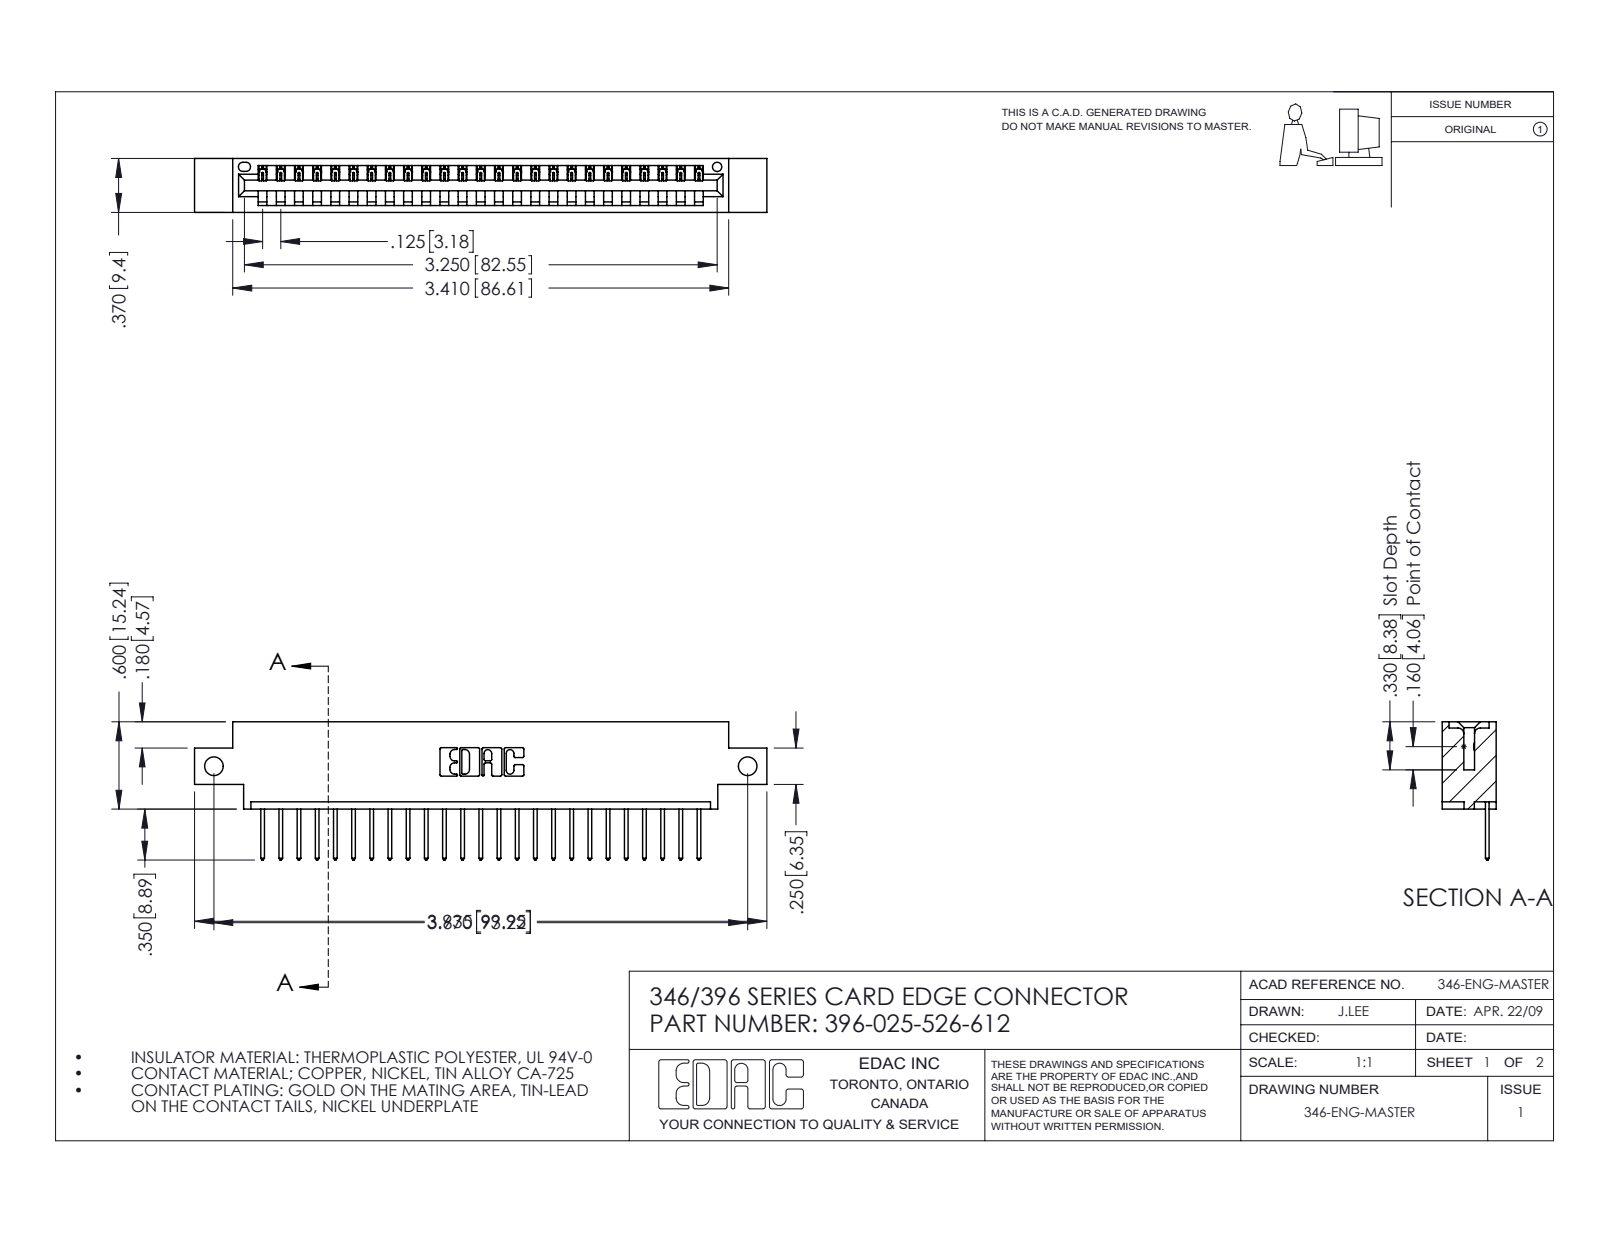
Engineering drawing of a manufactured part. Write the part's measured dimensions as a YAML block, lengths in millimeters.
part_name: "346 Part_0.170 Offset - Side Mount; 396-025-526-612; 345-292-001_345-293-126"
step_written_by: "SolidWorks 2016 (CONFIG_CONTROL_DESIGN)"
units: millimeters
bodies: {solids: 26, faces: 1576, planar: 1080, cylindrical: 496, other: 0}
overall_size: [99.9, 24.1, 9.4]
volume: 9190
surface_area: 11290
round_holes:
  - {diameter: 3.3, count: 2}
  - {diameter: 1.6, count: 1}
partial_cylinders:
  - {radius: 0.2, count: 50}
  - {radius: 0.3, count: 50}
  - {radius: 0.3, count: 22}
  - {radius: 0.2, count: 6}
  - {radius: 0.8, count: 6}
  - {radius: 0.7, count: 3}
  - {radius: 0.8, count: 2}
  - {radius: 1, count: 2}
face_to_face_distances: [1.2, 8.2, 9.4, 6.4, 1.8, 7.6, 0.6, 3.8, 5.6, 2.5]
hole_center_spacings: [93.2]
